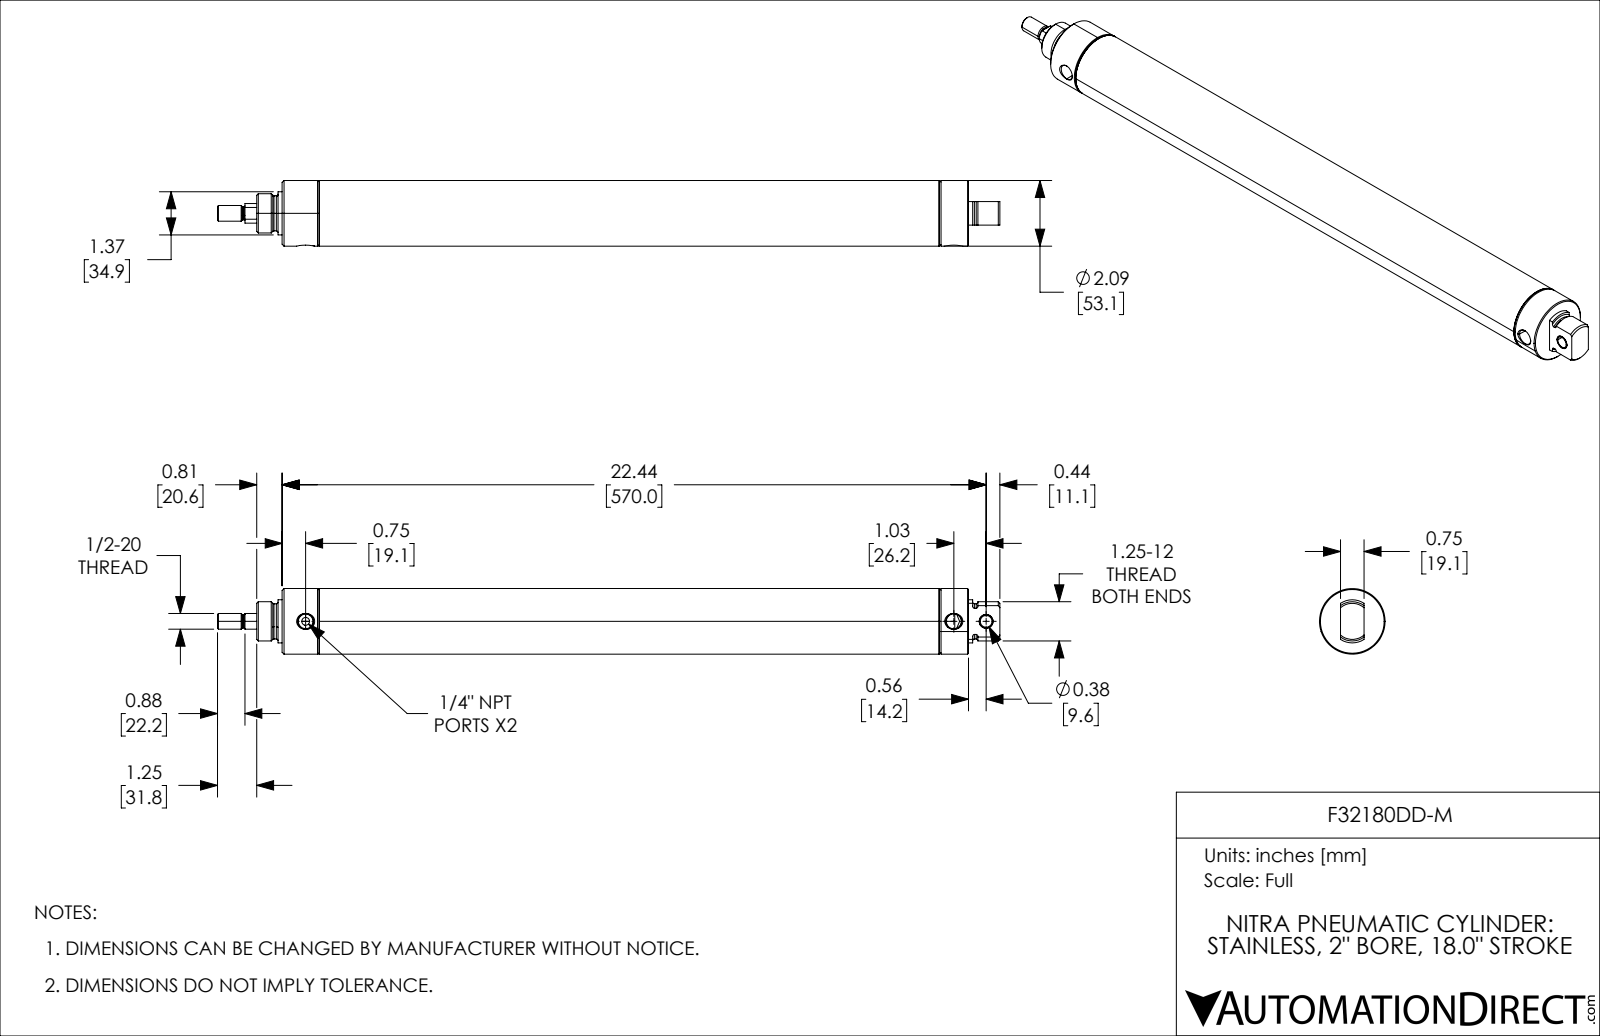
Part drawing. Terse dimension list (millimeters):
name: F32180DD-M_7; F32180DD-M_9; F32180DD-M_3; F32180DD-M (+2 more)
written by: SolidWorks 2021 (CONFIG_CONTROL_DESIGN)
unit: mm
bodies: 5 solids, 160 faces (31 planar, 60 cylindrical, 69 other)
size: 633.42 × 53.09 × 53.09
volume: 398 514 mm³; area: 234 580 mm²
holes: 1× ⌀6.35, 1× ⌀9.55, 1× ⌀11.15, 1× ⌀12.18, 1× ⌀16.52, 1× ⌀19.05, 1× ⌀49.05
bosses: 1× ⌀53.09, 1× ⌀51.16, 1× ⌀34.87, 1× ⌀31.75, 1× ⌀28.51, 1× ⌀15.88, 1× ⌀12.7, 1× ⌀10.46
rounds: 1× R14.25
face distances: 30.18, 457.2, 487.38, 517.6, 60.4, 30.22, 487.37, 30.17, 30.23, 38.15
hole spacings: 26.17, 524.76, 550.93
